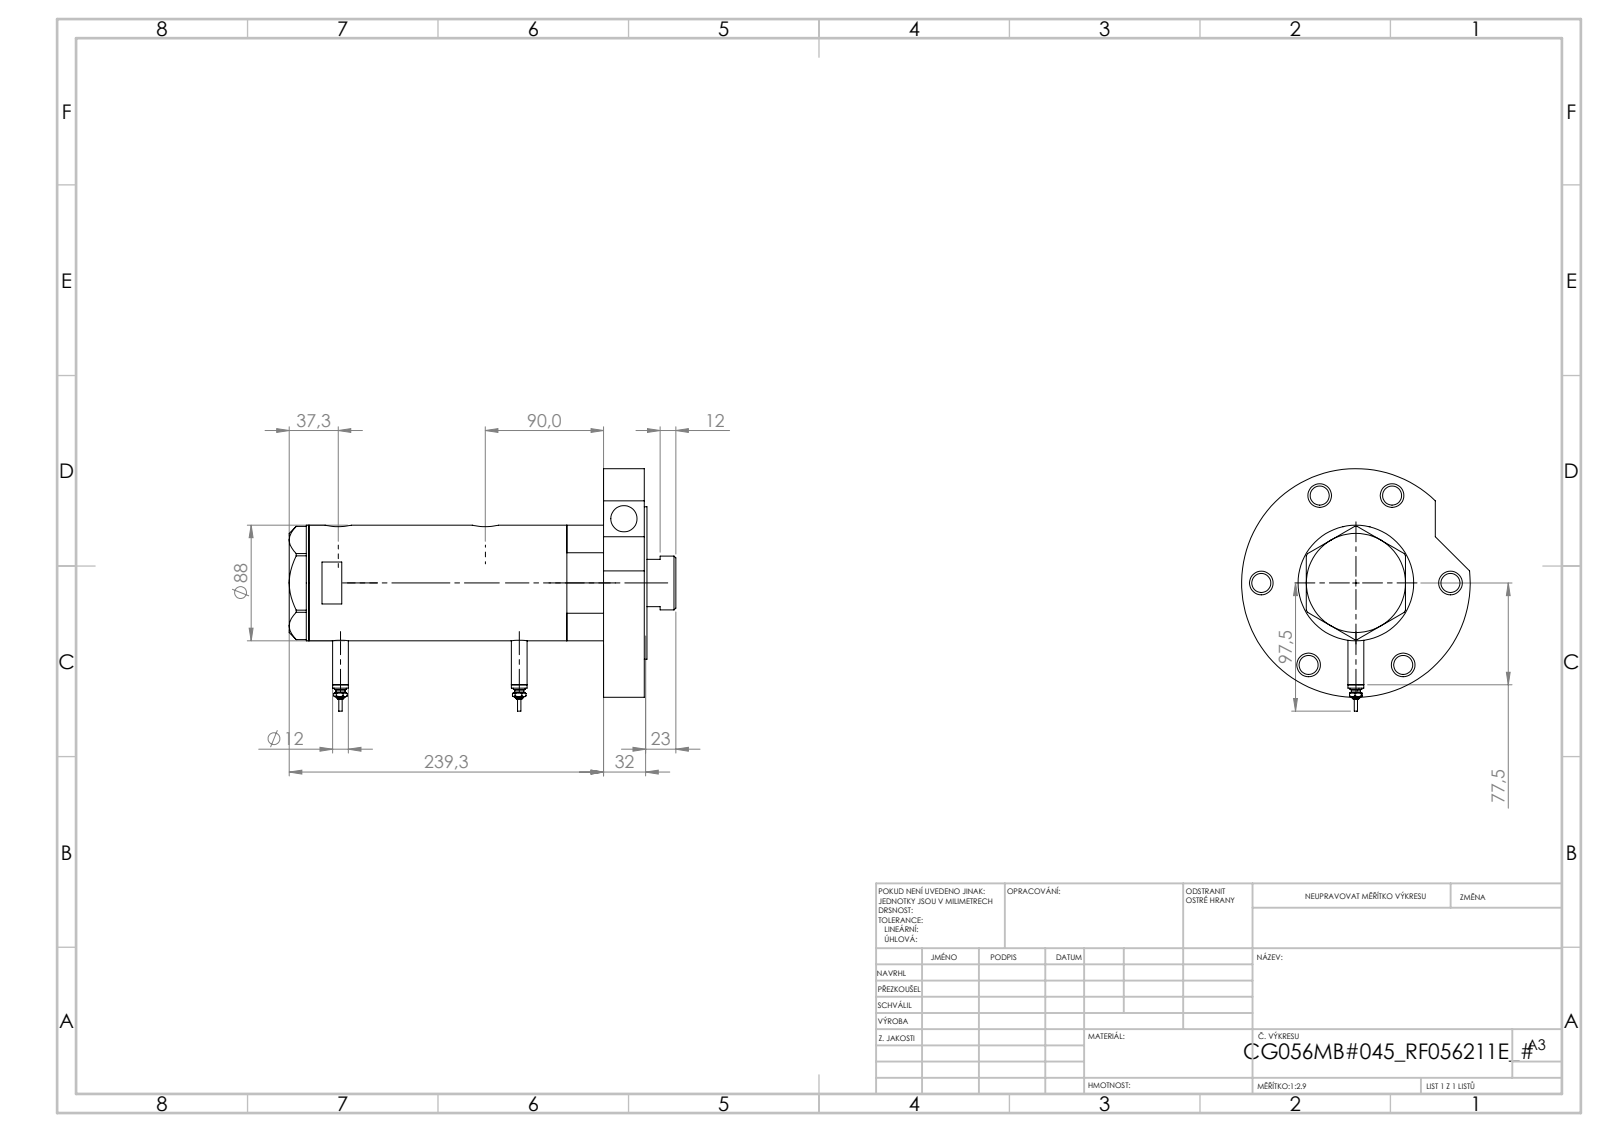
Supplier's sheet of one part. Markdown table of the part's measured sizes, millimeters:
| quantity | value |
| --- | --- |
| part name | Switch; V270CG_VC; V270CG_MIDDLE; V270CG_RF211E (+2 more) |
| STEP written by | SolidWorks 2019 (CONFIG_CONTROL_DESIGN) |
| units | millimeters |
| bodies | 7 solids, 257 faces (91 planar, 102 cylindrical, 64 other) |
| overall size | 294.3 × 184.5 × 174 |
| volume | 2 066 000 mm³ |
| surface area | 302 478 mm² |
| round holes (diameter × count) | 14.5 × 7, 18 × 6, 20 × 3, 12.5 × 2, 13.16 × 2, 42 × 1, 43.5 × 1, 56 × 1, 60 × 1, 75 × 1, 80 × 1 |
| round bosses / shafts (diameter × count) | 12 × 2, 9 × 2, 7 × 2, 4.5 × 2, 2.5 × 2, 174 × 1, 116 × 1, 88 × 1 |
| main face-to-face distances | 31, 2, 257.3, 224.3, 255.3, 33, 134.4, 89.9, 120.9, 122.9 |
| hole center spacings | 72, 80, 119.73, 124.71, 129.15, 143.69, 1.7, 25.8 |
